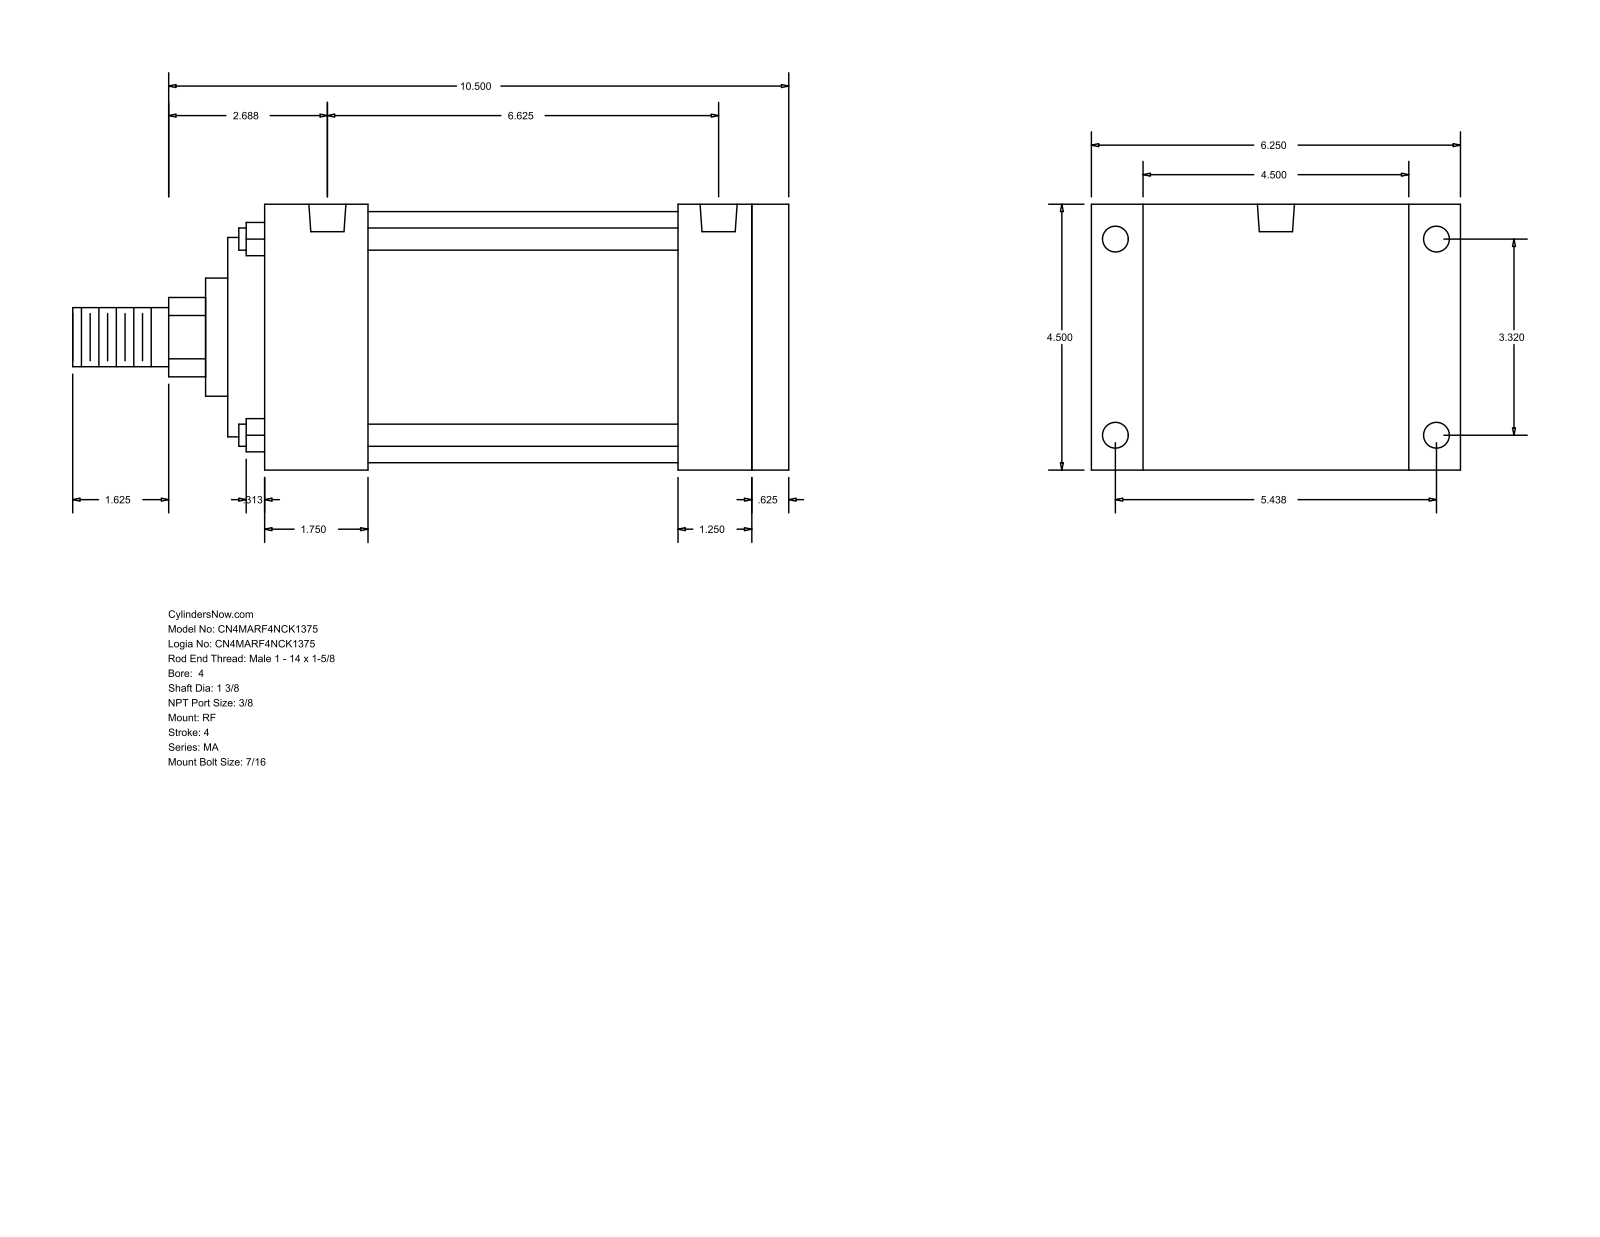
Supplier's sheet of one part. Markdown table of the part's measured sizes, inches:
| quantity | value |
| --- | --- |
| part name | MA_RF__0400_1.375 |
| STEP written by | GSSL Pune (CONFIG_CONTROL_DESIGN) |
| units | inches |
| bodies | 0 solids, 94 faces (65 planar, 29 cylindrical, 0 other) |
| overall size | 12.125 × 6.25 × 4.5 |
| round holes (diameter × count) | 0.437 × 8, 0.627 × 2 |
| round bosses / shafts (diameter × count) | 0.375 × 4, 4.25 × 1, 3.375 × 1, 2 × 1, 1.375 × 1, 1 × 1 |
| partial cylindrical surfaces (radius × count) | 0.672 × 1 |
| main face-to-face distances | 4.5, 8.875, 0.625, 8.25, 0.625, 8.875, 9.5, 0.875, 5.375, 7.625 |
| hole center spacings | 3.32, 5.438, 6.25, 6.371, 0.187, 0.188, 6.437, 6.438 |
